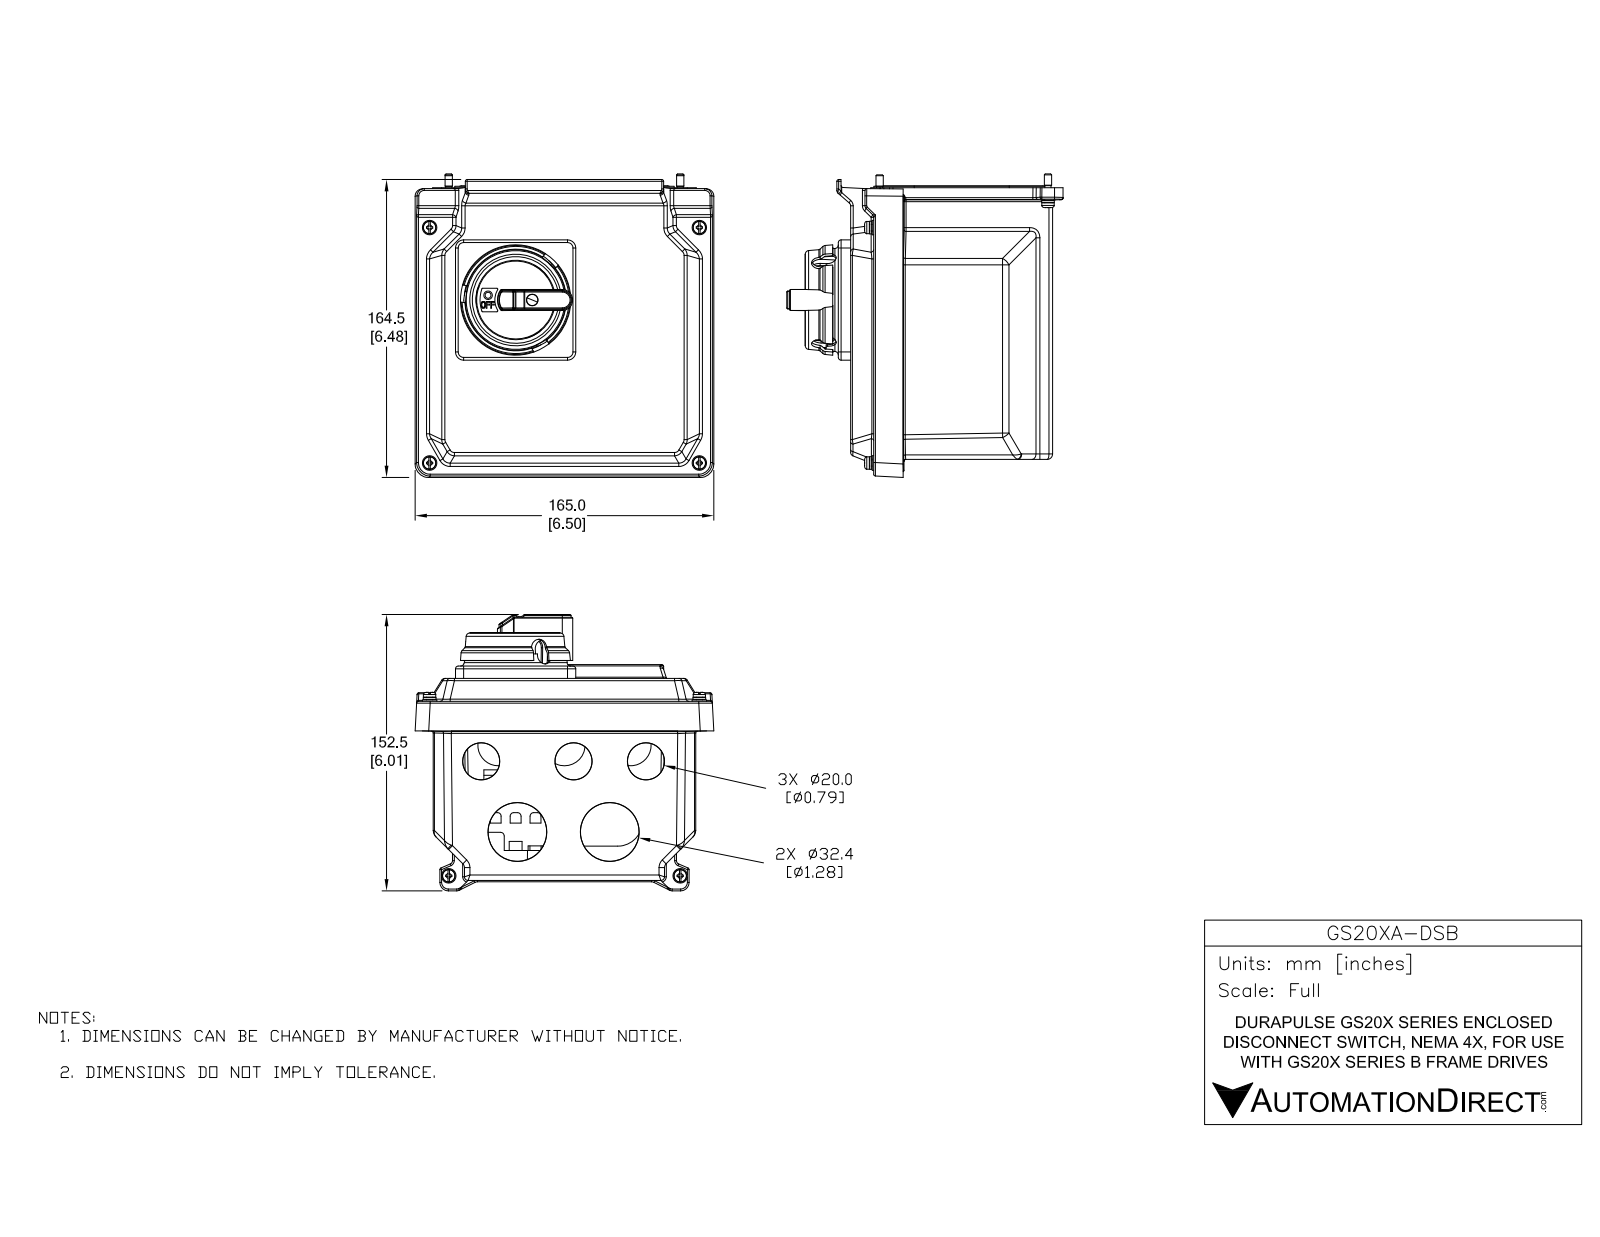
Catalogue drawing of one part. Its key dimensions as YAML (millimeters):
part_name: "GS20XA-DSB"
step_written_by: "SolidWorks 2017 (AUTOMOTIVE_DESIGN)"
units: millimeters
bodies: {solids: 32, faces: 2240, planar: 905, cylindrical: 700, other: 635}
overall_size: [167.6, 165, 152.6]
volume: 355400
surface_area: 278100
round_holes:
  - {diameter: 3.5, count: 8}
  - {diameter: 3.6, count: 8}
  - {diameter: 4.8, count: 4}
  - {diameter: 5.6, count: 4}
  - {diameter: 5.6, count: 4}
  - {diameter: 5.7, count: 3}
  - {diameter: 6.4, count: 3}
  - {diameter: 15, count: 3}
  - {diameter: 3.3, count: 2}
  - {diameter: 8, count: 2}
  - {diameter: 4.7, count: 1}
  - {diameter: 6.2, count: 1}
round_bosses_or_shafts:
  - {diameter: 7, count: 8}
  - {diameter: 6.8, count: 8}
  - {diameter: 4, count: 8}
  - {diameter: 3.4, count: 8}
  - {diameter: 8, count: 6}
  - {diameter: 25.1, count: 3}
  - {diameter: 23.6, count: 3}
  - {diameter: 19.8, count: 3}
partial_cylinders:
  - {radius: 0.5, count: 99}
  - {radius: 1, count: 59}
  - {radius: 2, count: 55}
  - {radius: 5, count: 28}
  - {radius: 2.5, count: 17}
  - {radius: 3, count: 14}
  - {radius: 0.2, count: 13}
  - {radius: 1.5, count: 11}
face_to_face_distances: [2.5, 109, 111.6, 106.6, 96.3, 12.7, 23.5, 2.8, 26, 146]
hole_center_spacings: [33.9, 48, 14.3, 28.2, 32, 35.5, 41, 55.5]
